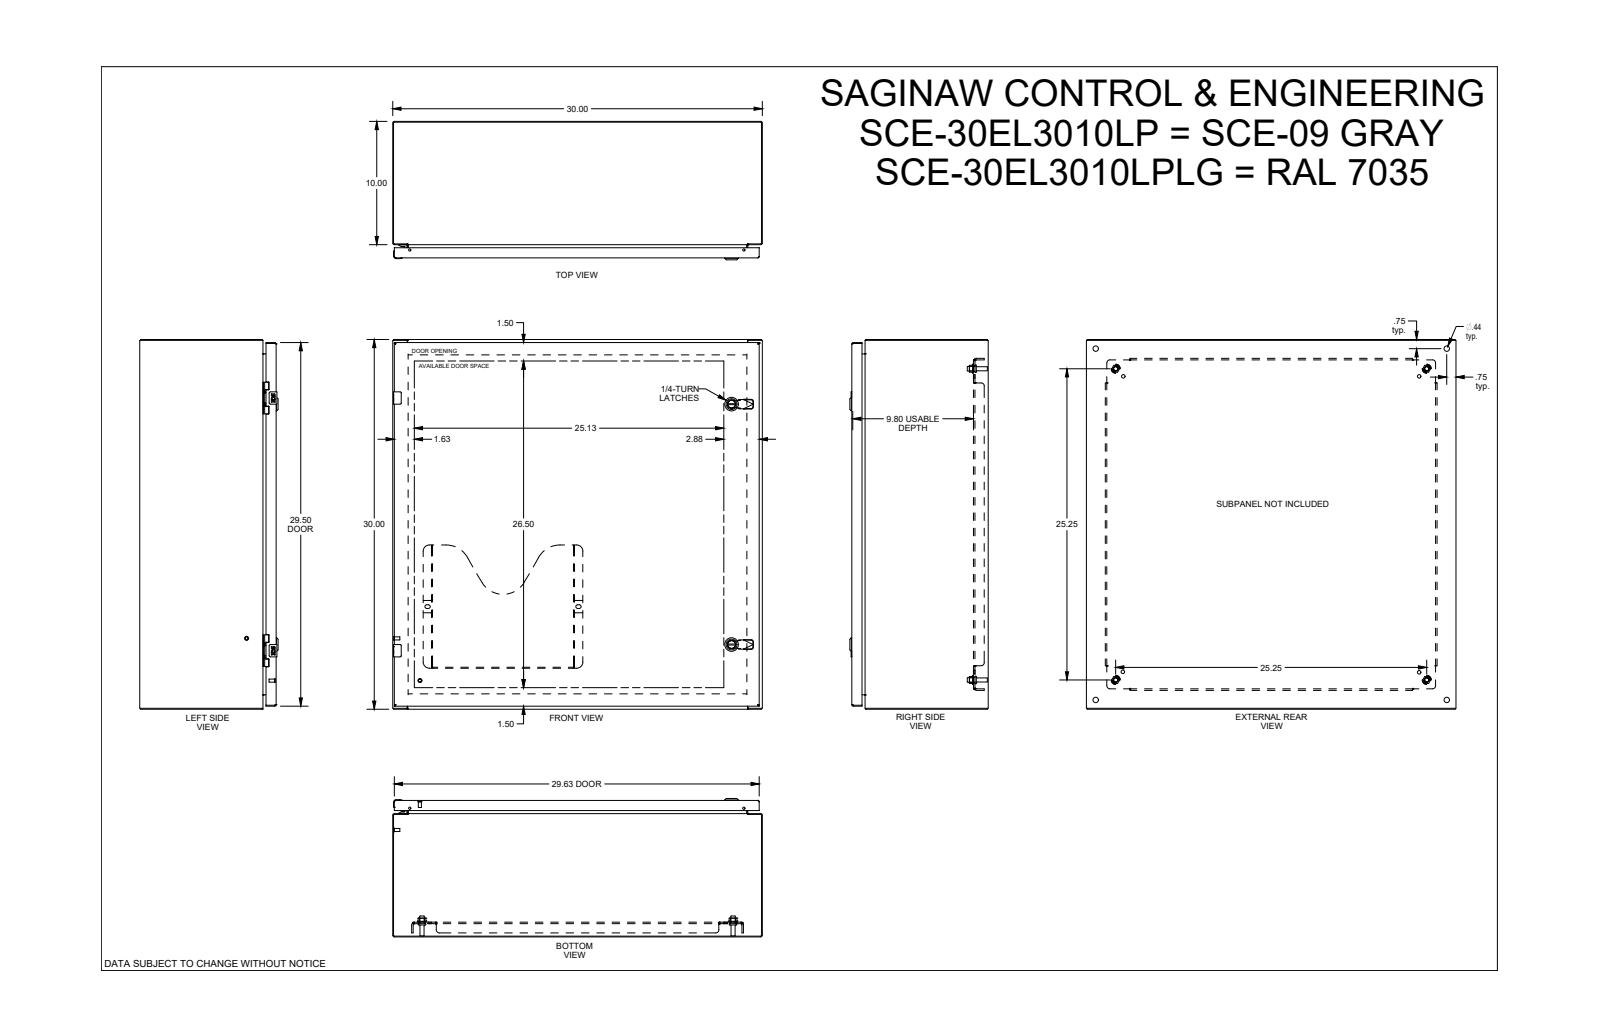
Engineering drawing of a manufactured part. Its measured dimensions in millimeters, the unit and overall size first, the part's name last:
Units: millimetres
Overall size (bounding box): 762 × 762 × 285.2
Round holes (diameter × count): ⌀4.4 ×4, ⌀5.2 ×4, ⌀6.2 ×4, ⌀6.8 ×4, ⌀7.1 ×4, ⌀9.3 ×4, ⌀9.5 ×4, ⌀11.1 ×4, ⌀12.7 ×4, ⌀1 ×2, ⌀4.8 ×2, ⌀5 ×2
Round bosses / shafts (diameter × count): ⌀4.3 ×6, ⌀9.3 ×4, ⌀8.4 ×4, ⌀6.4 ×4, ⌀6.3 ×4, ⌀6.1 ×4, ⌀5 ×3, ⌀28 ×2
Partial cylindrical surfaces — rounded edges, fillets, slot ends (radius × count): R0.3 ×56, R0.3 ×28, R0.4 ×20, R0.5 ×20, R1 ×17, R1.5 ×13, R0.7 ×12, R2.5 ×12
Main face-to-face distances: 1.9, 760.1, 1.5, 281.3, 279.3, 279.7, 277.8, 30.5, 250.8, 25.4
Hole centre spacings: 683.9, 625.8, 641.4, 22.2, 25, 520.7, 669.3, 0.5
Volume: 6 027 000 mm³ · Surface area: 5 634 000 mm²
Bodies: 47 solids, 2843 faces (1115 planar, 858 cylindrical, 870 other)
Part name (STEP PRODUCT): SCE-30EL3010LP
STEP written by: SolidWorks 2021 (AUTOMOTIVE_DESIGN)
